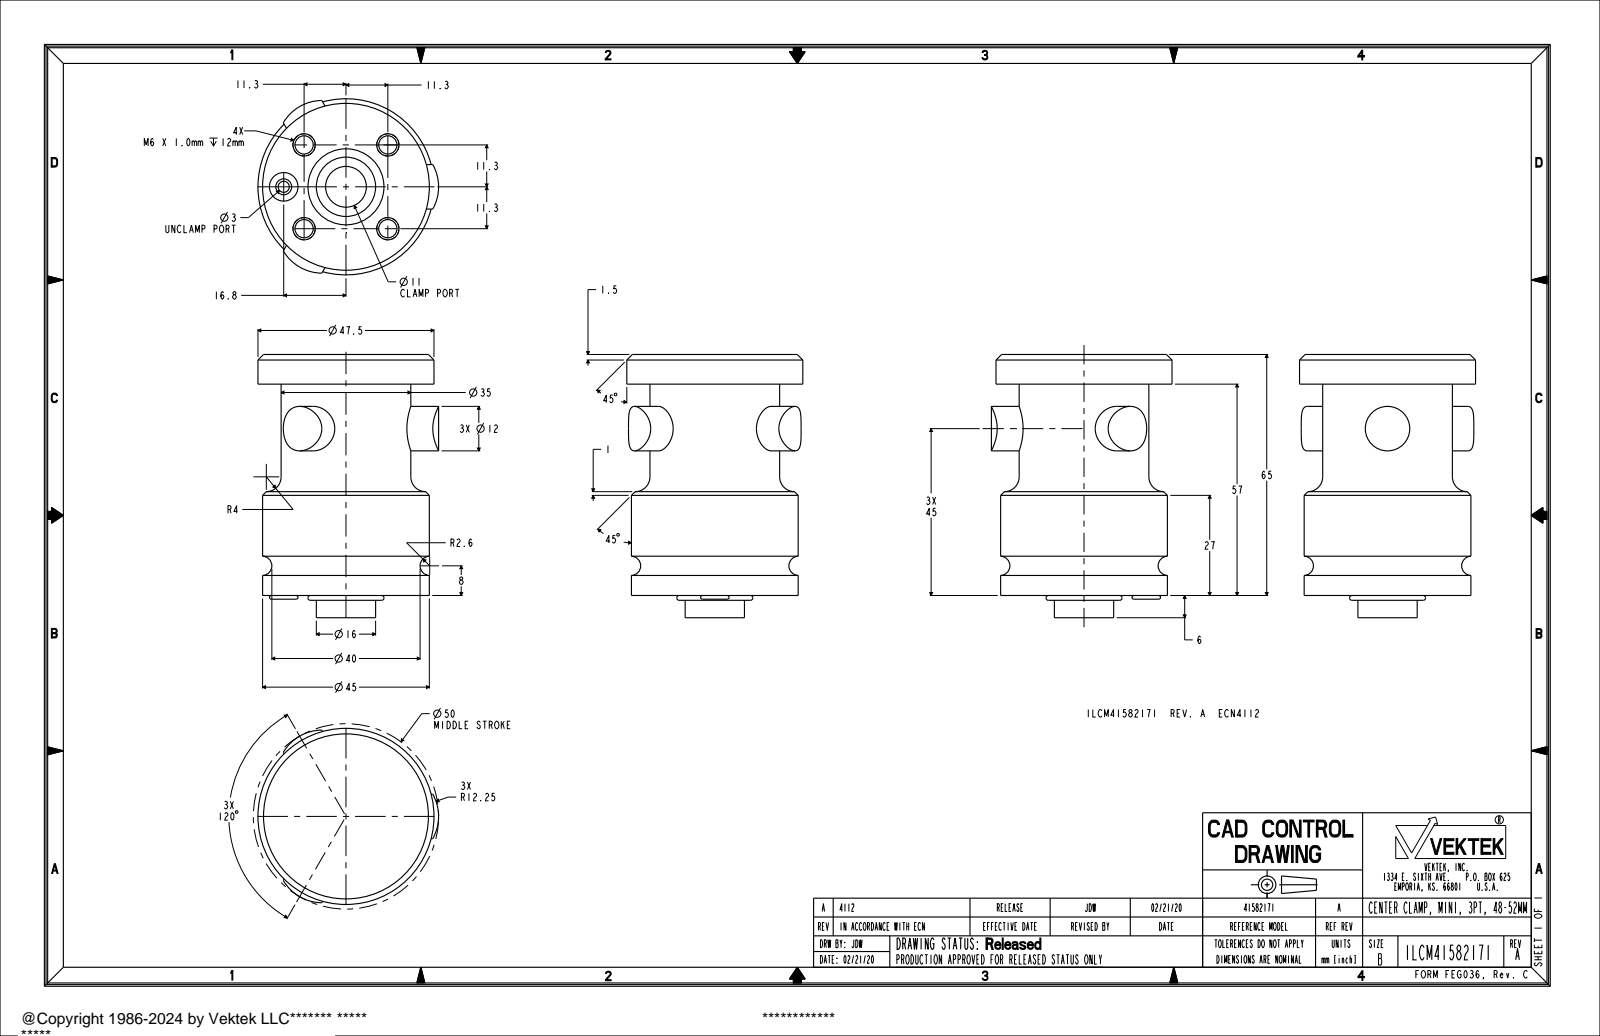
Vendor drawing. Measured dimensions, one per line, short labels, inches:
name: ILCM41582171
written by: PRO/ENGINEER BY PARAMETRIC TECHNOLOGY CORPORATION, 2013320 (AUTOMOTIVE_DESIGN)
unit: in
bodies: 1 solid, 97 faces (18 planar, 43 cylindrical, 36 other)
size: 2.795 × 1.919 × 1.87
volume: 5.352 in³; area: 25.67 in²
holes: 4× ⌀0.194, 1× ⌀0.118, 1× ⌀0.433
bosses: 4× ⌀0.236, 3× ⌀0.472, 1× ⌀1.87, 1× ⌀1.772, 1× ⌀1.378, 1× ⌀0.807, 1× ⌀0.63
rounds: 3× R0.482
face distances: 2.559, 0.315, 2.244, 2.48, 0.039, 2.283, 2.598, 0.197, 0.236, 2.795
hole spacings: 0.629, 0.89, 0.495, 1.193, 1.258, 0.661
